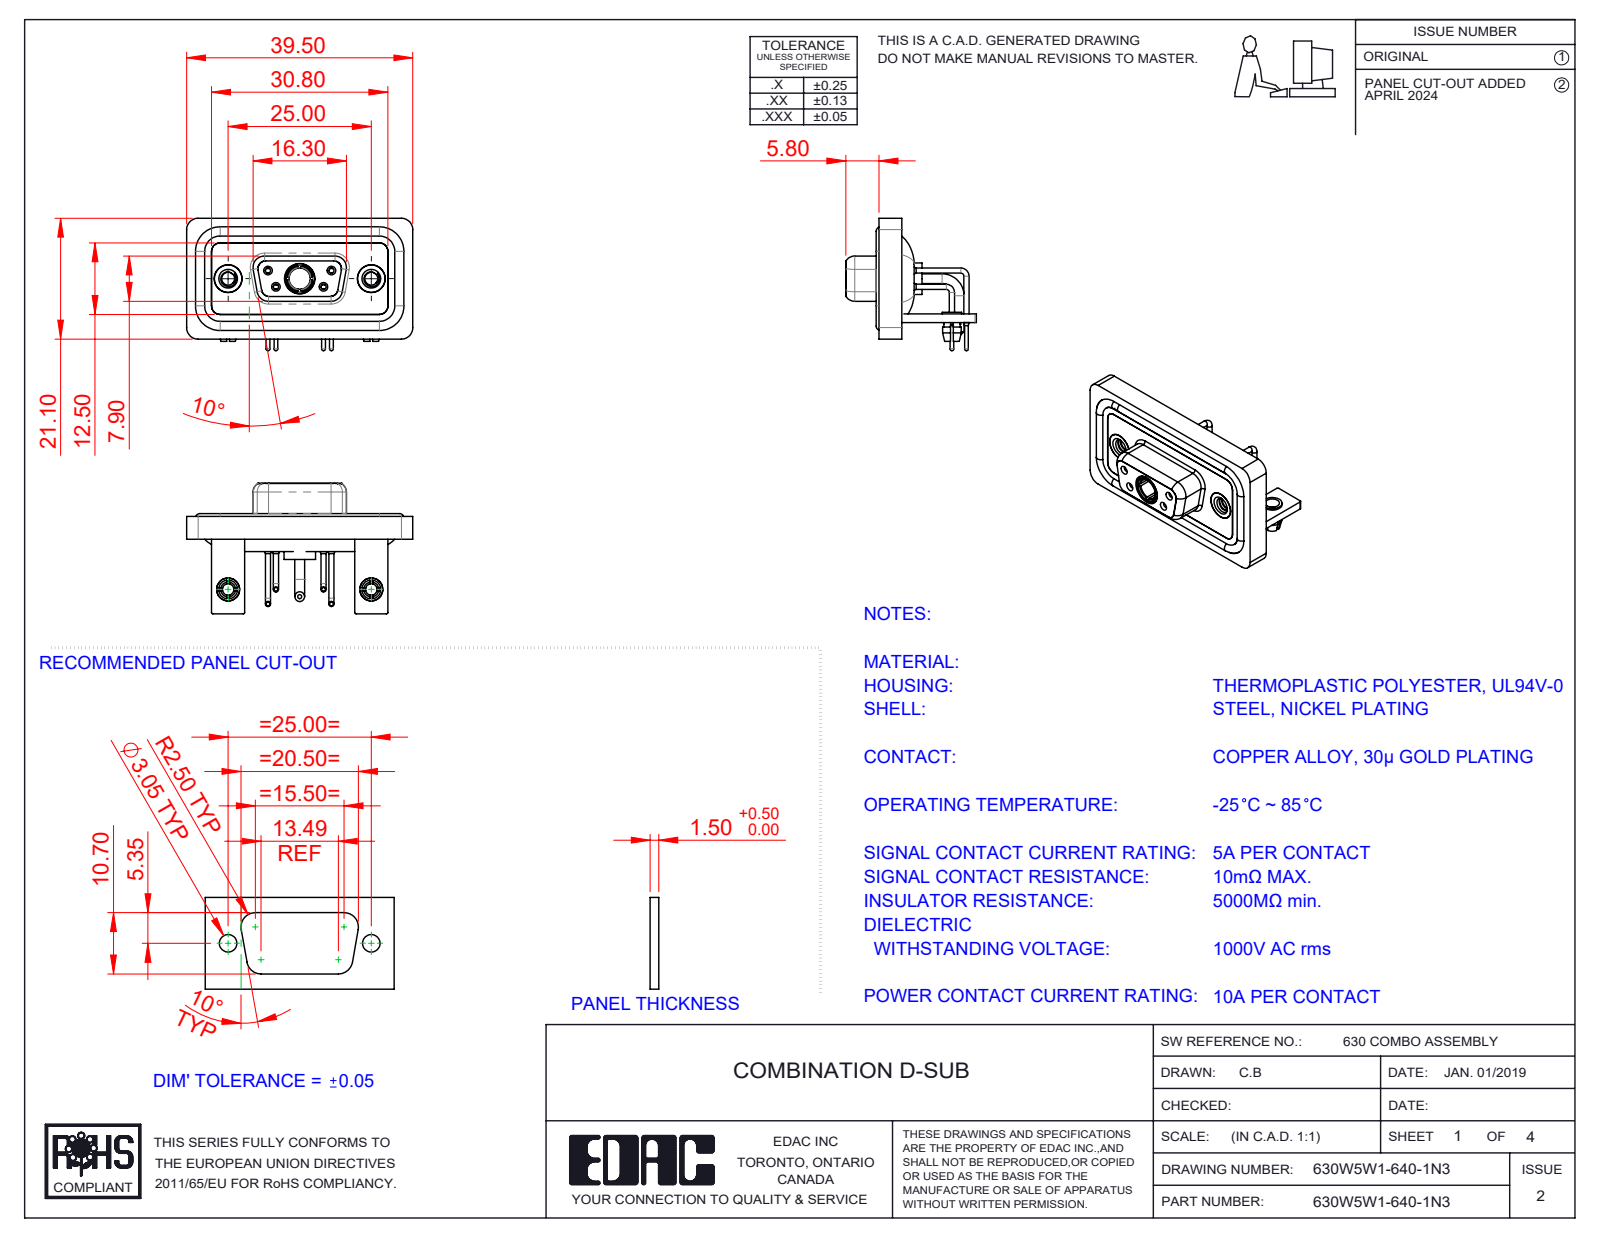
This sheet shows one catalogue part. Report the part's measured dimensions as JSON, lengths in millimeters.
{"part_name": "630Combo Board Lock_50 Contacts; 630Combo Contact Row 1_50 Contacts; Power Socket_10A RA; 630Combo Contact Row 2_50 Contacts (+7 more)", "step_written_by": "SolidWorks 2023 (CONFIG_CONTROL_DESIGN)", "units": "millimeters", "bodies": {"solids": 17, "faces": 816, "planar": 262, "cylindrical": 361, "other": 193}, "overall_size": [39.5, 23.12, 22.8], "volume_mm3": 5174, "surface_area_mm2": 8738, "round_holes": [[2, 6], [0.9, 4], [1.1, 4], [1.5, 4], [4.85, 3], [1.6, 2], [1.7, 2], [2.26, 2], [2.5, 2], [3.2, 2], [4, 2], [4.05, 2]], "round_bosses_or_shafts": [[1.6, 6], [0.9, 4], [0.65, 4], [4.95, 2], [4.8, 2], [4, 2], [3.4, 2], [3.3, 2]], "partial_cylinders_radius": [[2, 19], [1.5, 18], [0.25, 16], [1.35, 8], [1.6, 8], [0.5, 5], [0.6, 4], [0.65, 4]], "face_to_face_distances": [0.4, 2.9, 1.5, 1.8, 1.1, 3.7, 1.6, 0.8, 2.5, 3.1], "hole_center_spacings": [3.16, 5.72, 7.1, 12.5, 18.1, 25, 4.39, 4.4]}
